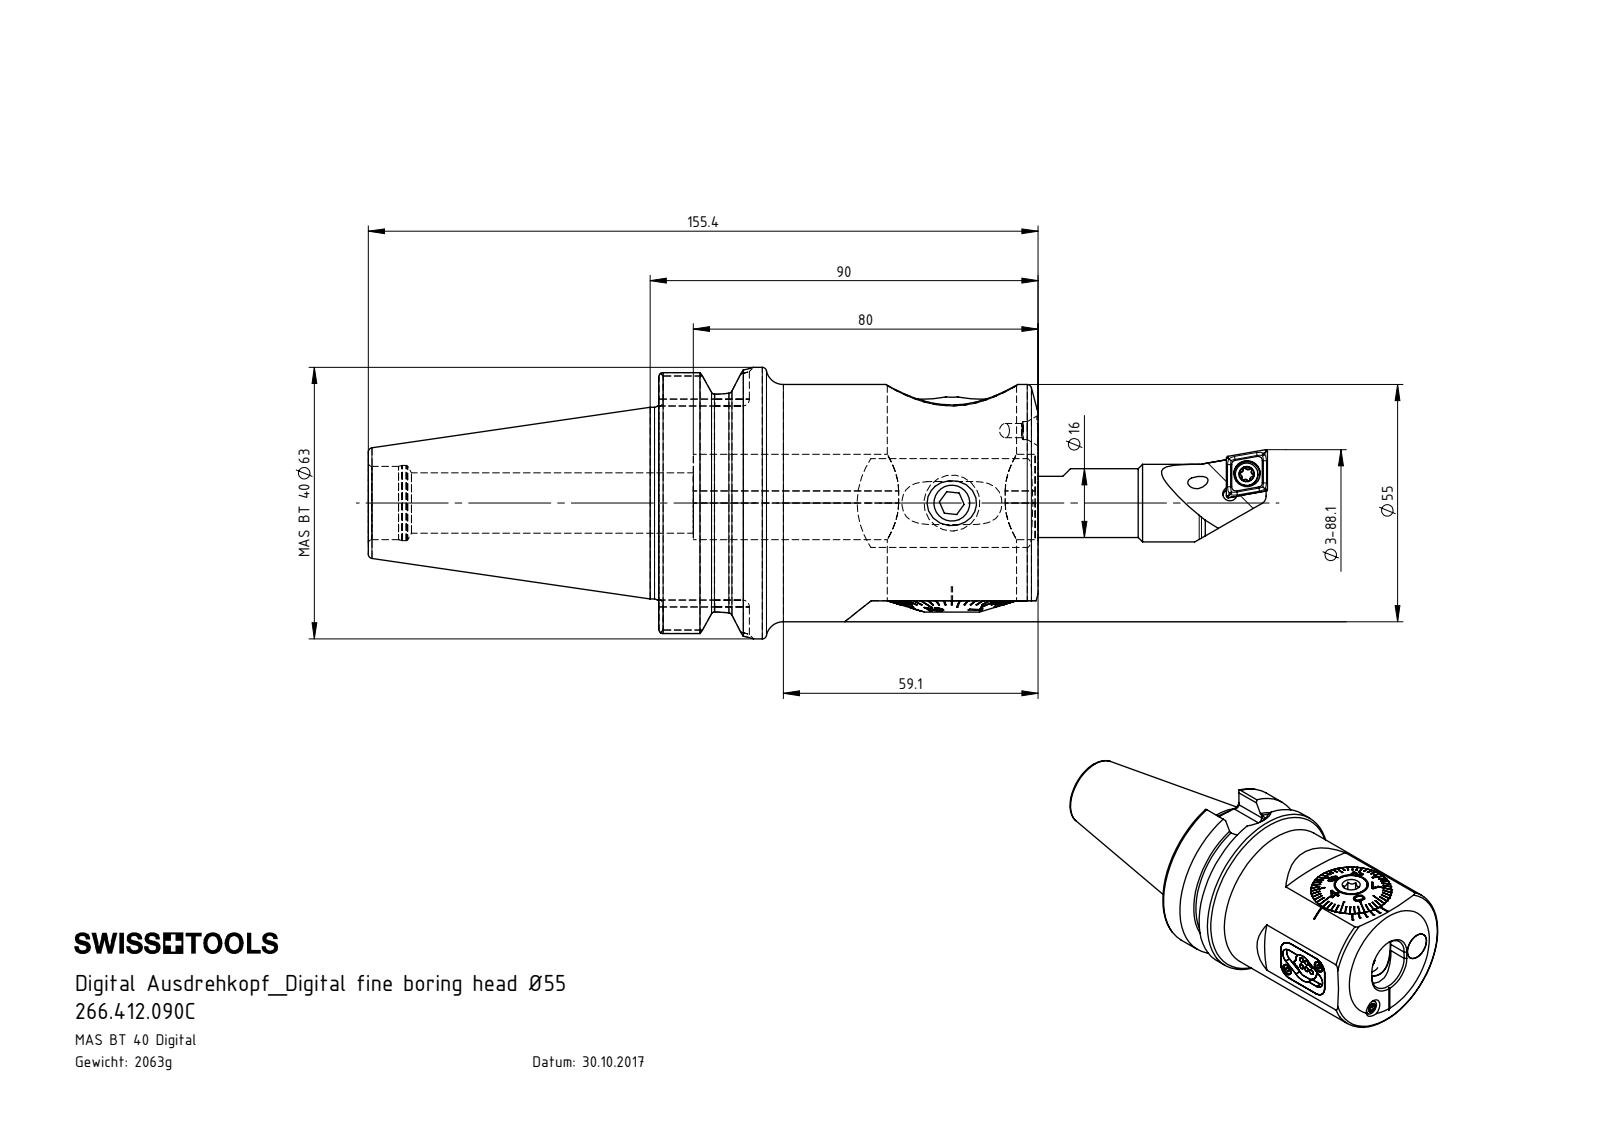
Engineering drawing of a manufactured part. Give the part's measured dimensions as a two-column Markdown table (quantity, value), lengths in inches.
| quantity | value |
| --- | --- |
| part name | PEF-DA1.011.017_A; CCMT09T304; A55-BG2.012.006_B; Klebstoff D10 (+8 more) |
| STEP written by | SolidWorks 2017 (CONFIG_CONTROL_DESIGN) |
| units | inches |
| bodies | 27 solids, 1179 faces (485 planar, 309 cylindrical, 385 other) |
| overall size | 8.215 × 2.48 × 2.48 |
| volume | 16.1 in³ |
| surface area | 104.4 in² |
| round holes (diameter × count) | 0.126 × 4, 0.063 × 3, 0.13 × 3, 0.165 × 3, 0.335 × 3, 0.087 × 2, 0.118 × 2, 0.551 × 2, 0.173 × 1, 0.24 × 1, 0.315 × 1, 0.394 × 1 |
| round bosses / shafts (diameter × count) | 0.075 × 6, 0.394 × 3, 0.709 × 2, 0.207 × 2, 0.157 × 2, 0.15 × 2, 0.079 × 2, 2.48 × 1 |
| partial cylindrical surfaces (radius × count) | 0.013 × 12, 0.023 × 12, 0.047 × 8, 0.063 × 8, 0.043 × 6, 0.177 × 4, 0.126 × 3, 0.173 × 3 |
| main face-to-face distances | 3.465, 0.146, 0.079, 0.157, 1.136, 0.018, 0.11, 0.209, 0.047, 0.222 |
| hole center spacings | 0.161, 0.17, 0.285, 0.333, 0.375, 0.472, 0.499, 0.571 |
